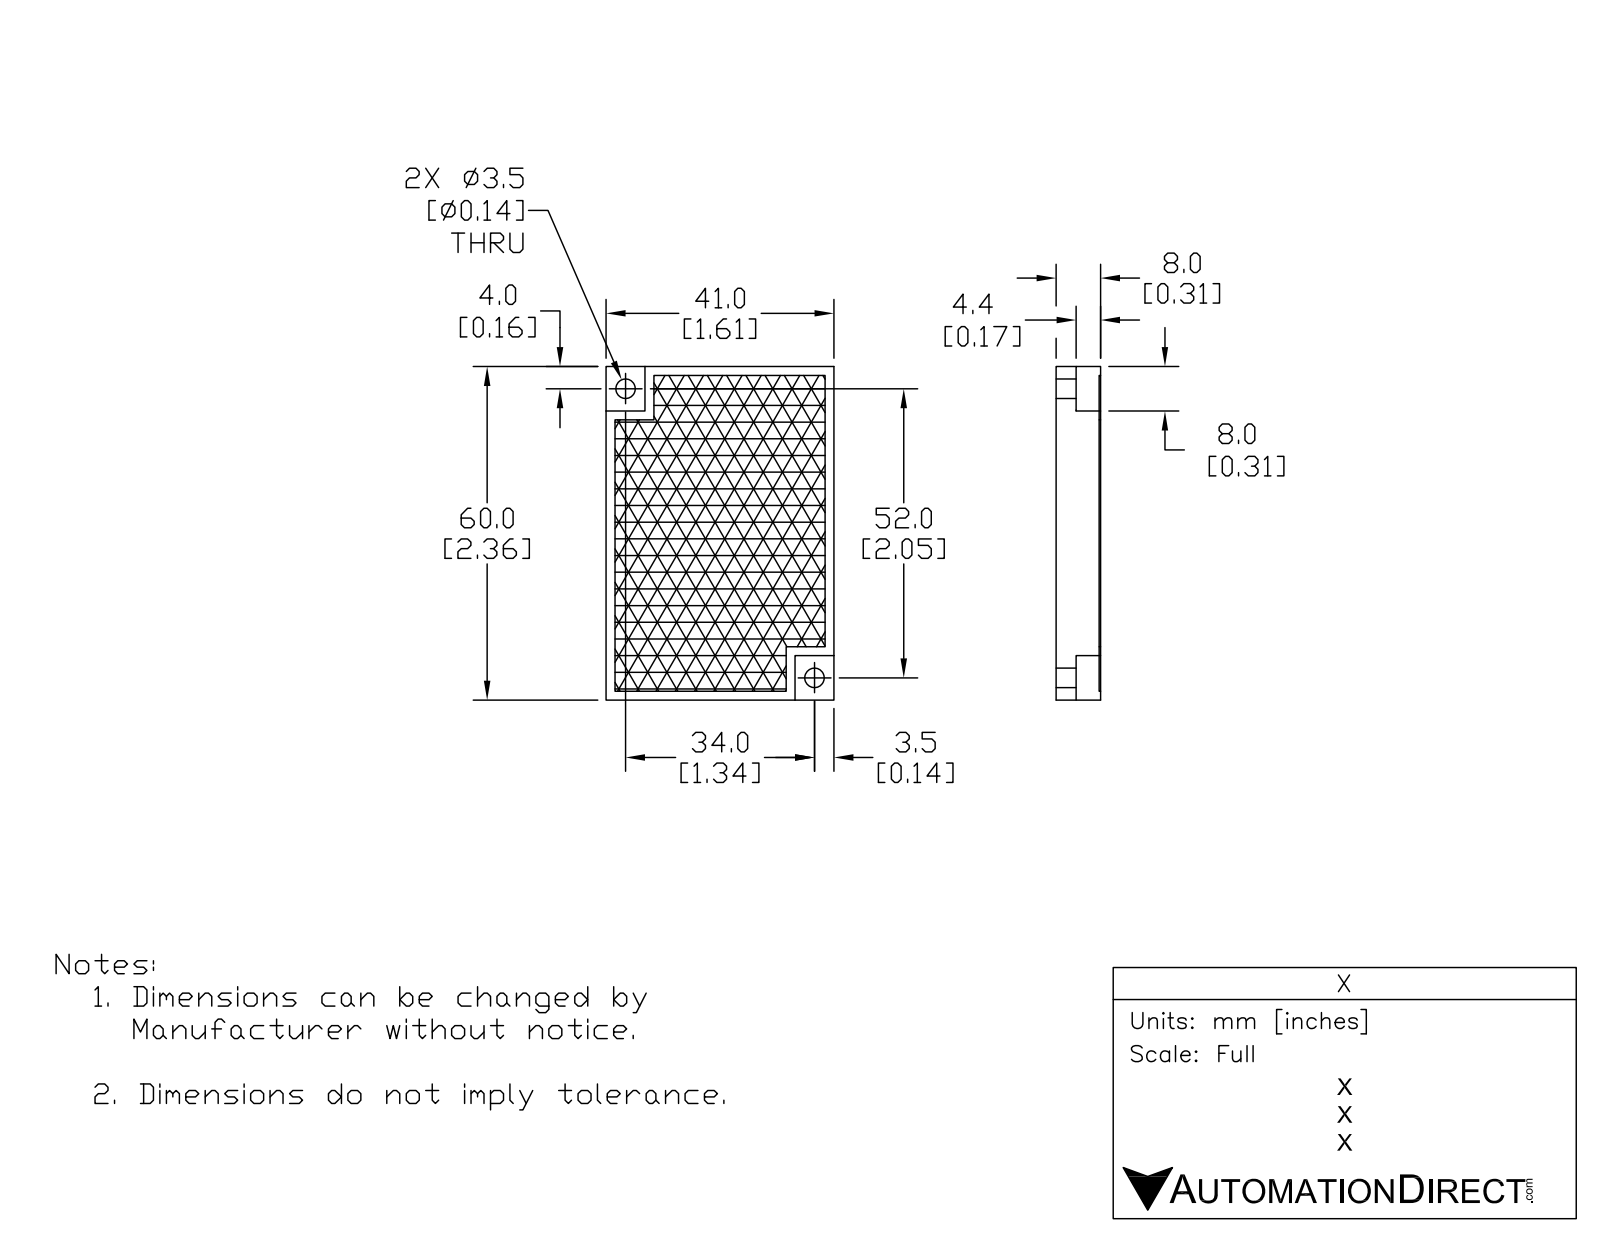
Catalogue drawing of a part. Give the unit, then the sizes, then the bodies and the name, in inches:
Units: inches
Overall size (bounding box): 2.362 × 1.614 × 0.295
Round holes (diameter × count): ⌀0.138 ×2
Main face-to-face distances: 0.287, 1.614, 0.295, 2.362, 0.138, 0.15, 0.157, 0.276, 1.339, 0.315
Hole centre spacings: 2.446
Volume: 1.07 in³ · Surface area: 10.09 in²
Bodies: 1 solid, 25 faces (21 planar, 4 cylindrical, 0 other)
Part name (STEP PRODUCT): RL-116
STEP written by: SolidWorks 2017 (AUTOMOTIVE_DESIGN)
